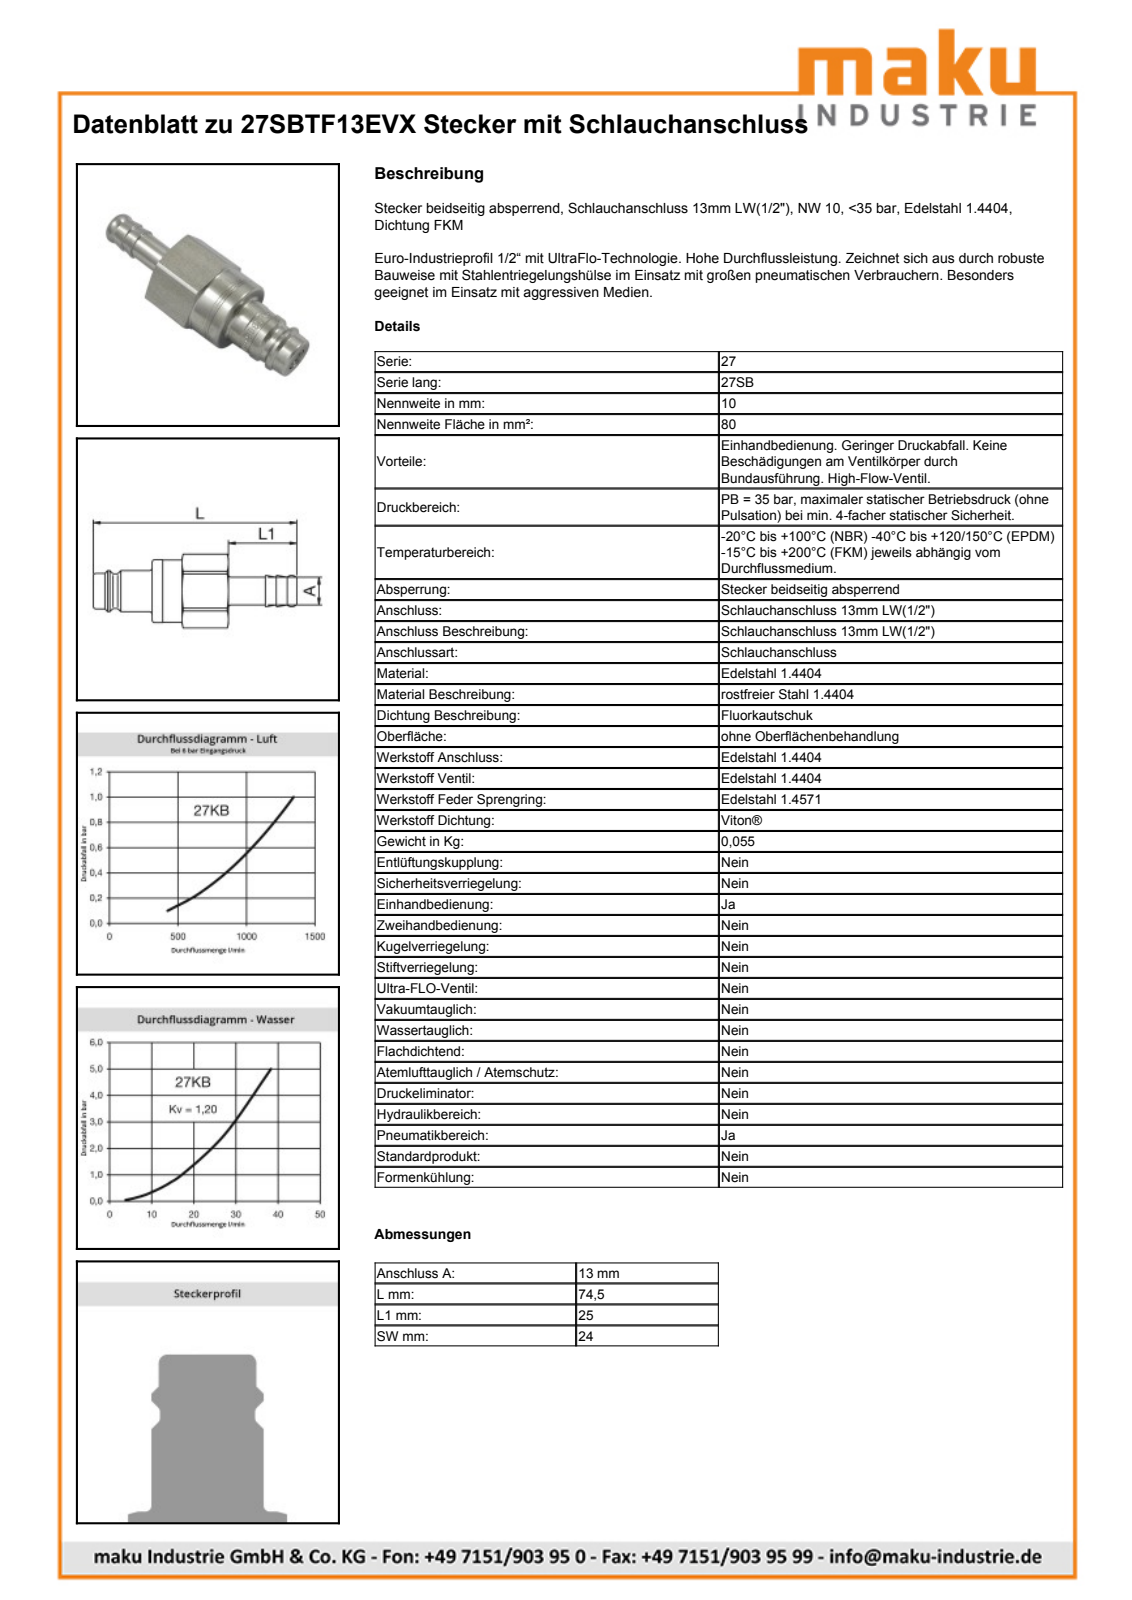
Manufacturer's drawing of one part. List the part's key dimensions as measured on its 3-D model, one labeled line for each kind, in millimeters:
Part name (STEP PRODUCT): D106462
STEP written by: Autodesk Inventor 2011 (AUTOMOTIVE_DESIGN)
Units: millimetres
Bodies: 1 solid, 63 faces (16 planar, 18 cylindrical, 29 other)
Overall size (bounding box): 74.4 × 27.04 × 24.84
Volume: 19 840 mm³ · Surface area: 5 908 mm²
Round holes (diameter × count): ⌀19 ×1, ⌀20.3 ×1
Round bosses / shafts (diameter × count): ⌀23 ×1, ⌀22.75 ×1, ⌀18.87 ×1, ⌀18.5 ×1, ⌀15 ×1, ⌀13.1 ×1, ⌀13 ×1, ⌀12.65 ×1
Partial cylindrical surfaces — rounded edges, fillets, slot ends (radius × count): R13.53 ×1
Main face-to-face distances: 24, 25, 27.9, 52.9, 21.5, 49.4, 74.4, 25.4, 3.9, 49
